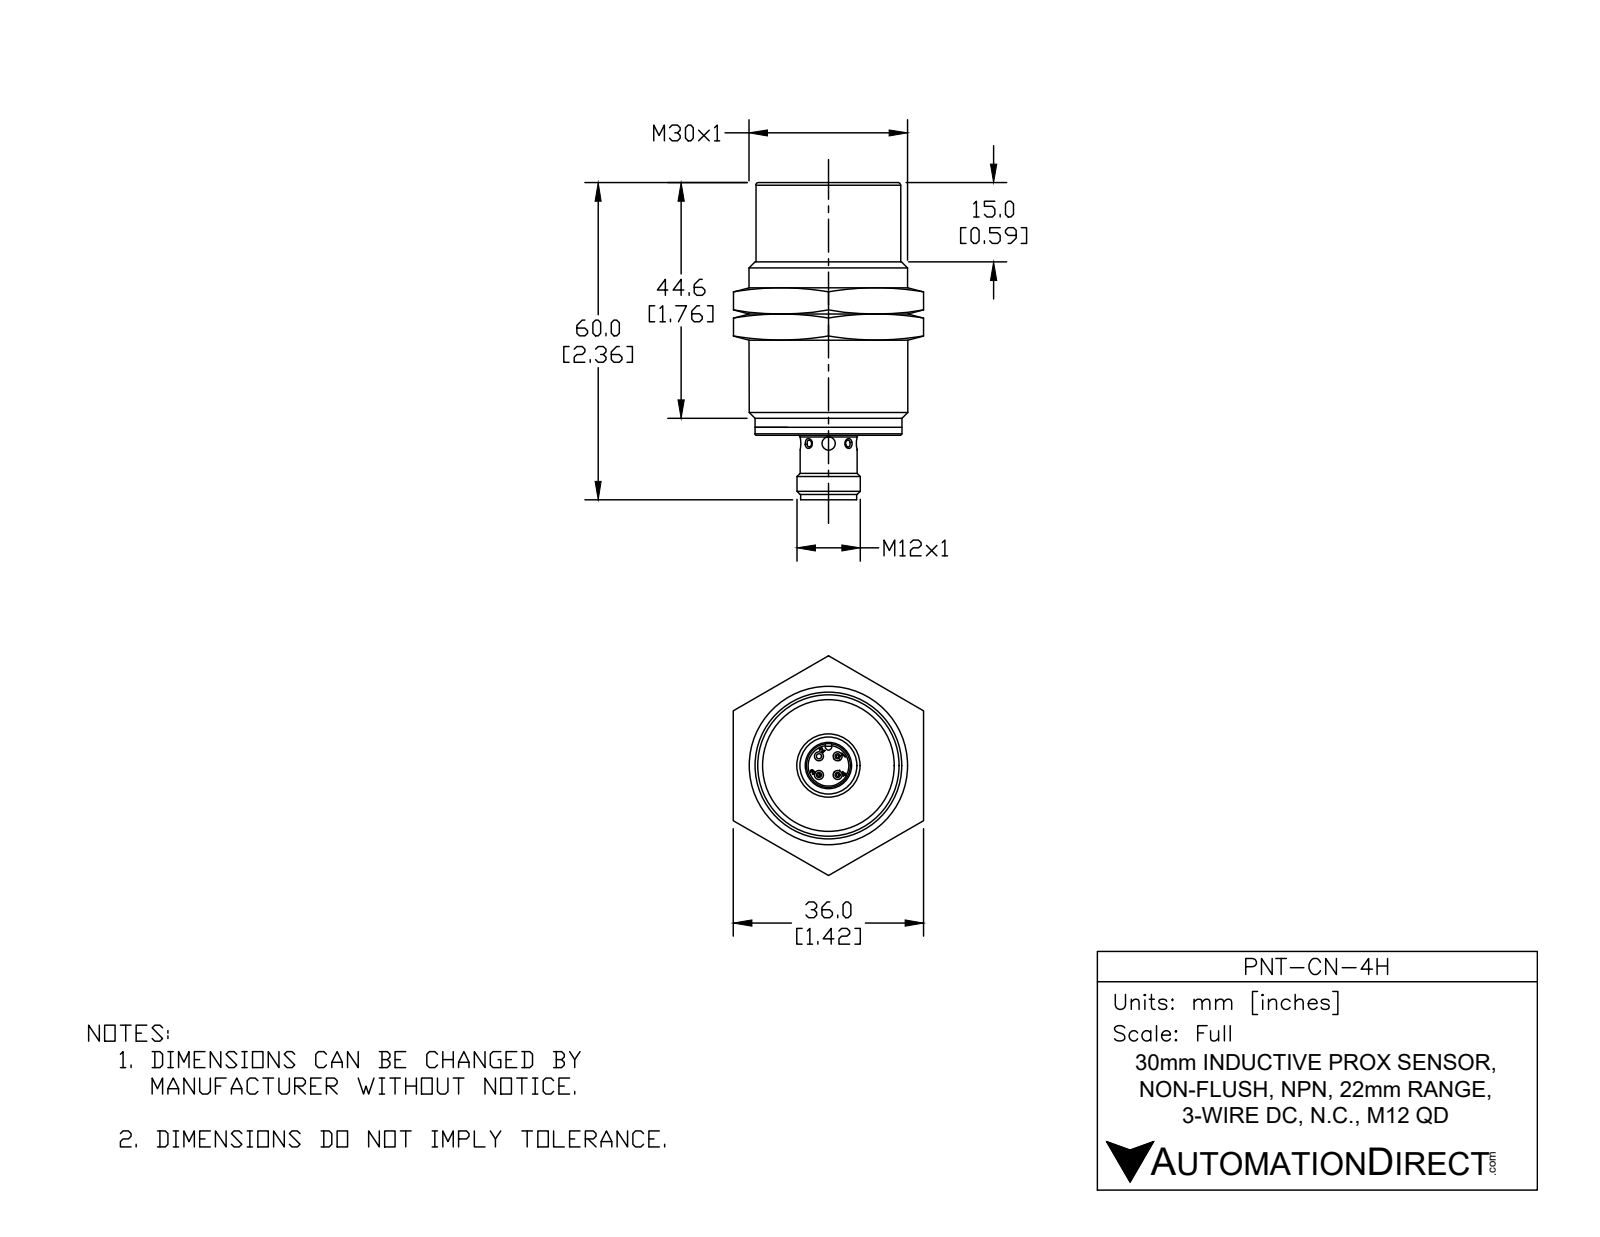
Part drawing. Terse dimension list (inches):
name: PNT-CN-4H
written by: SolidWorks 2017 (AUTOMOTIVE_DESIGN)
unit: in
bodies: 1 solid, 660 faces (260 planar, 164 cylindrical, 236 other)
size: 2.362 × 1.181 × 1.181
volume: 1.934 in³; area: 25.17 in²
holes: 3× ⌀0.043, 2× ⌀0.04, 2× ⌀0.098, 1× ⌀0.038, 1× ⌀0.04, 1× ⌀0.323, 1× ⌀0.327, 1× ⌀0.394, 1× ⌀1.047, 1× ⌀1.076
bosses: 9× ⌀0.039, 1× ⌀1.181, 1× ⌀1.094, 1× ⌀1.083, 1× ⌀1.074, 1× ⌀1.044, 1× ⌀1.037, 1× ⌀1.021
rounds: 12× R0.004, 8× R0.02, 6× R0.157, 3× R0.03, 3× R0.039, 1× R0.024, 1× R0.031
face distances: 0.157, 1.882, 1.724, 0.037, 0.12, 1.844, 1.854, 0.13, 0.031, 0.028
hole spacings: 0.098, 0.139, 0.197
